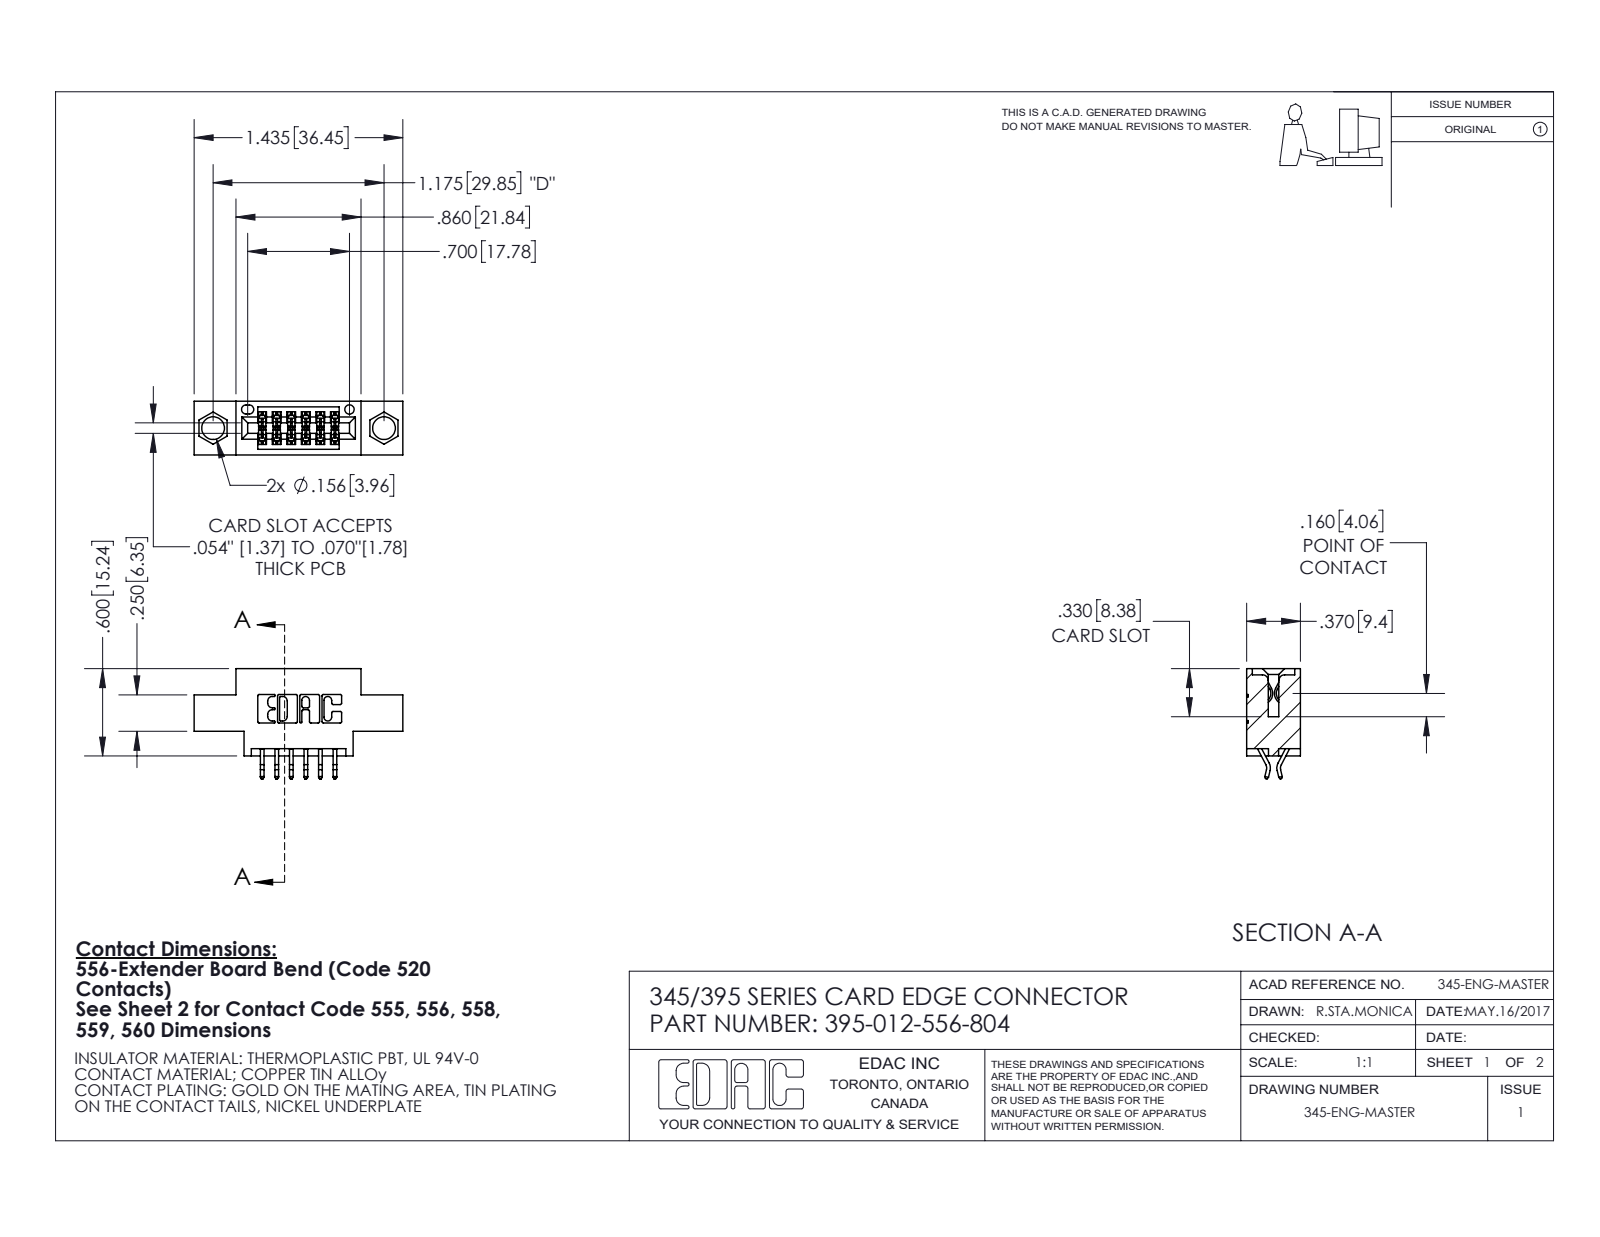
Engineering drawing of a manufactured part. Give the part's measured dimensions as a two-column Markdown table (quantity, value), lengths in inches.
| quantity | value |
| --- | --- |
| part name | 395-012-556-804; 345 Part_0.170 Offset - 0.156 Dia-TI; 345-292-001_556 Tail |
| STEP written by | SolidWorks 2020 (CONFIG_CONTROL_DESIGN) |
| units | inches |
| bodies | 13 solids, 816 faces (542 planar, 274 cylindrical, 0 other) |
| overall size | 1.435 × 0.757 × 0.37 |
| volume | 0.182 in³ |
| surface area | 5.738 in² |
| round holes (diameter × count) | 0.156 × 2, 0.064 × 1 |
| partial cylindrical surfaces (radius × count) | 0.006 × 24, 0.01 × 22, 0.007 × 6, 0.031 × 6, 0.026 × 3, 0.01 × 2, 0.014 × 2, 0.019 × 2 |
| main face-to-face distances | 0.37, 0.2, 0.072, 0.298, 0.1, 0.025, 0.098, 0.272, 0.06, 0.3 |
| hole center spacings | 0.27, 0.946, 1.175 |
